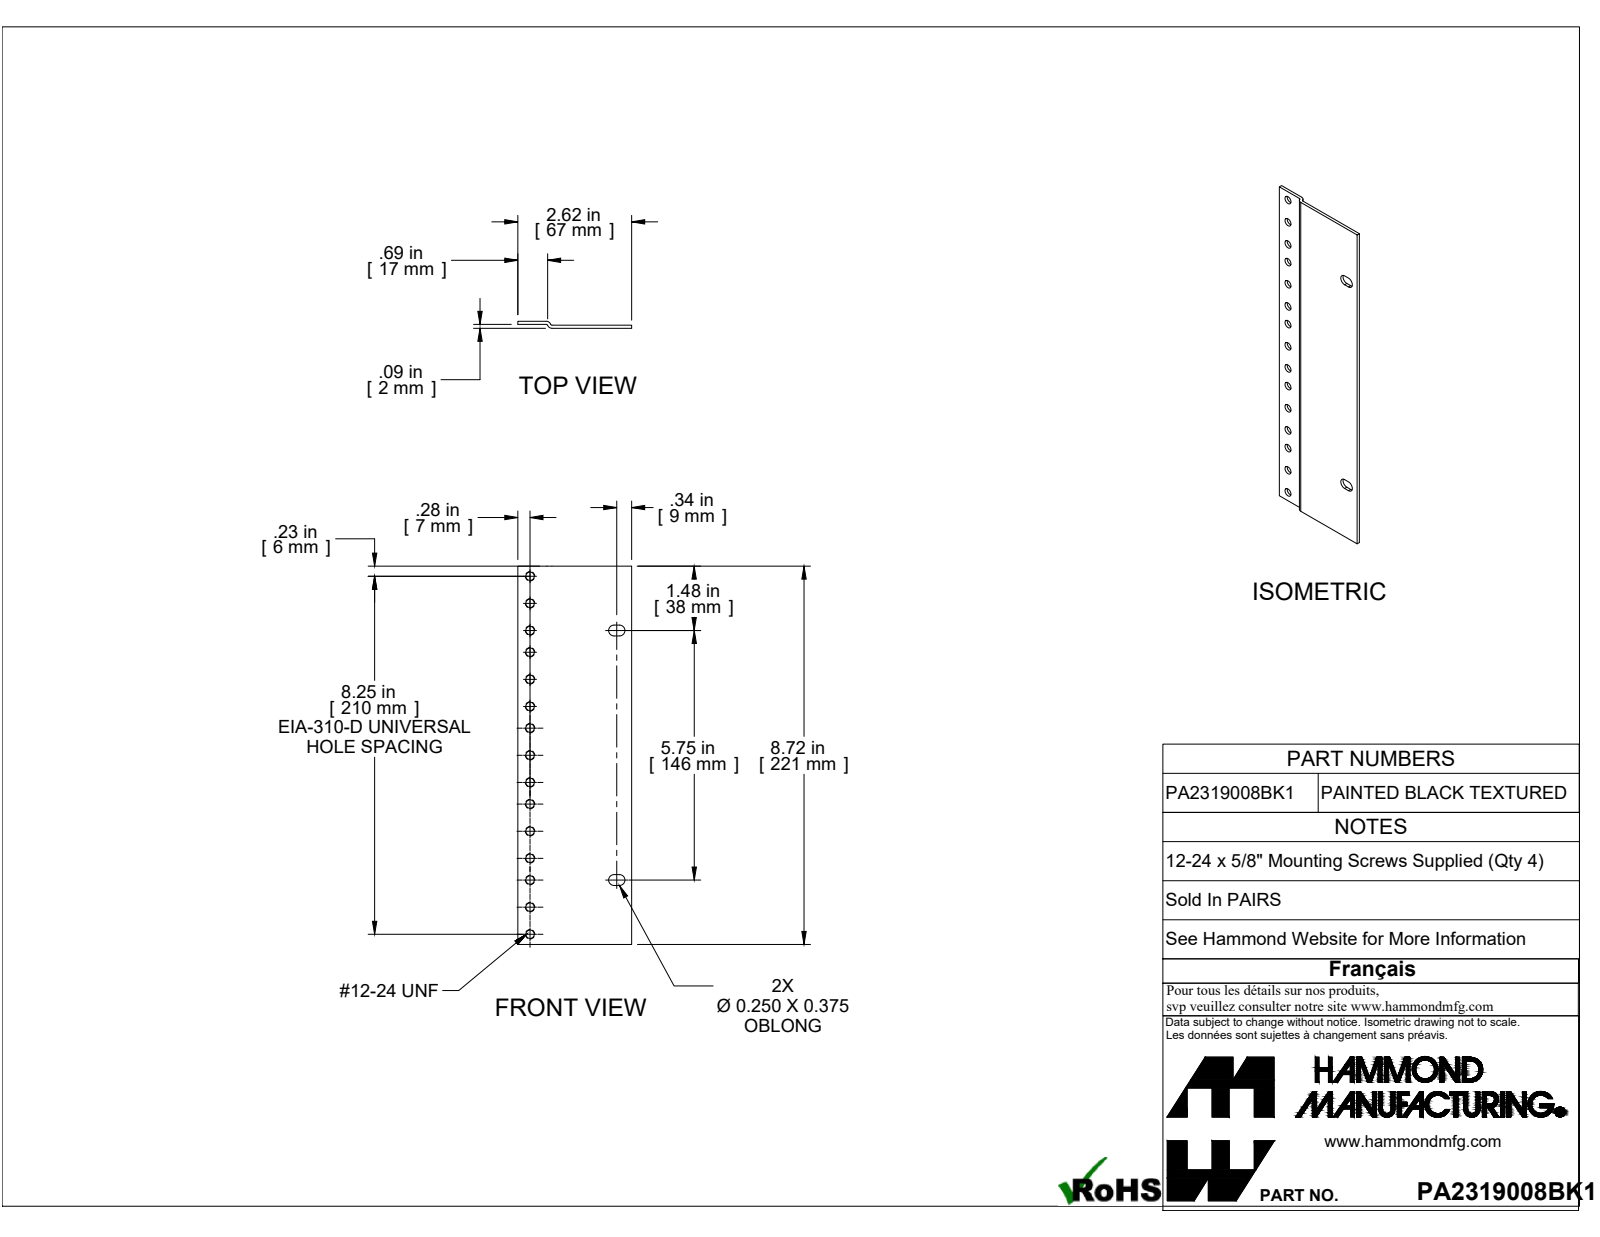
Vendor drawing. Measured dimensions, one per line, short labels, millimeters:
name: PA2319008BK1
written by: SolidWorks 2019 (AUTOMOTIVE_DESIGN)
unit: mm
bodies: 1 solid, 35 faces (12 planar, 23 cylindrical, 0 other)
size: 221.4 × 66.7 × 4.1
volume: 26 680 mm³; area: 30 750 mm²
holes: 15× ⌀4.9
rounds: 4× R3.2, 2× R0.9, 2× R2.7
face distances: 1.8, 2.3, 4.1, 0.5, 2.3, 1.8, 66.7, 221.4, 34.5, 40.9
hole spacings: 44.5, 15.9, 15.9, 28.6, 28.6, 60.3, 60.3, 73
